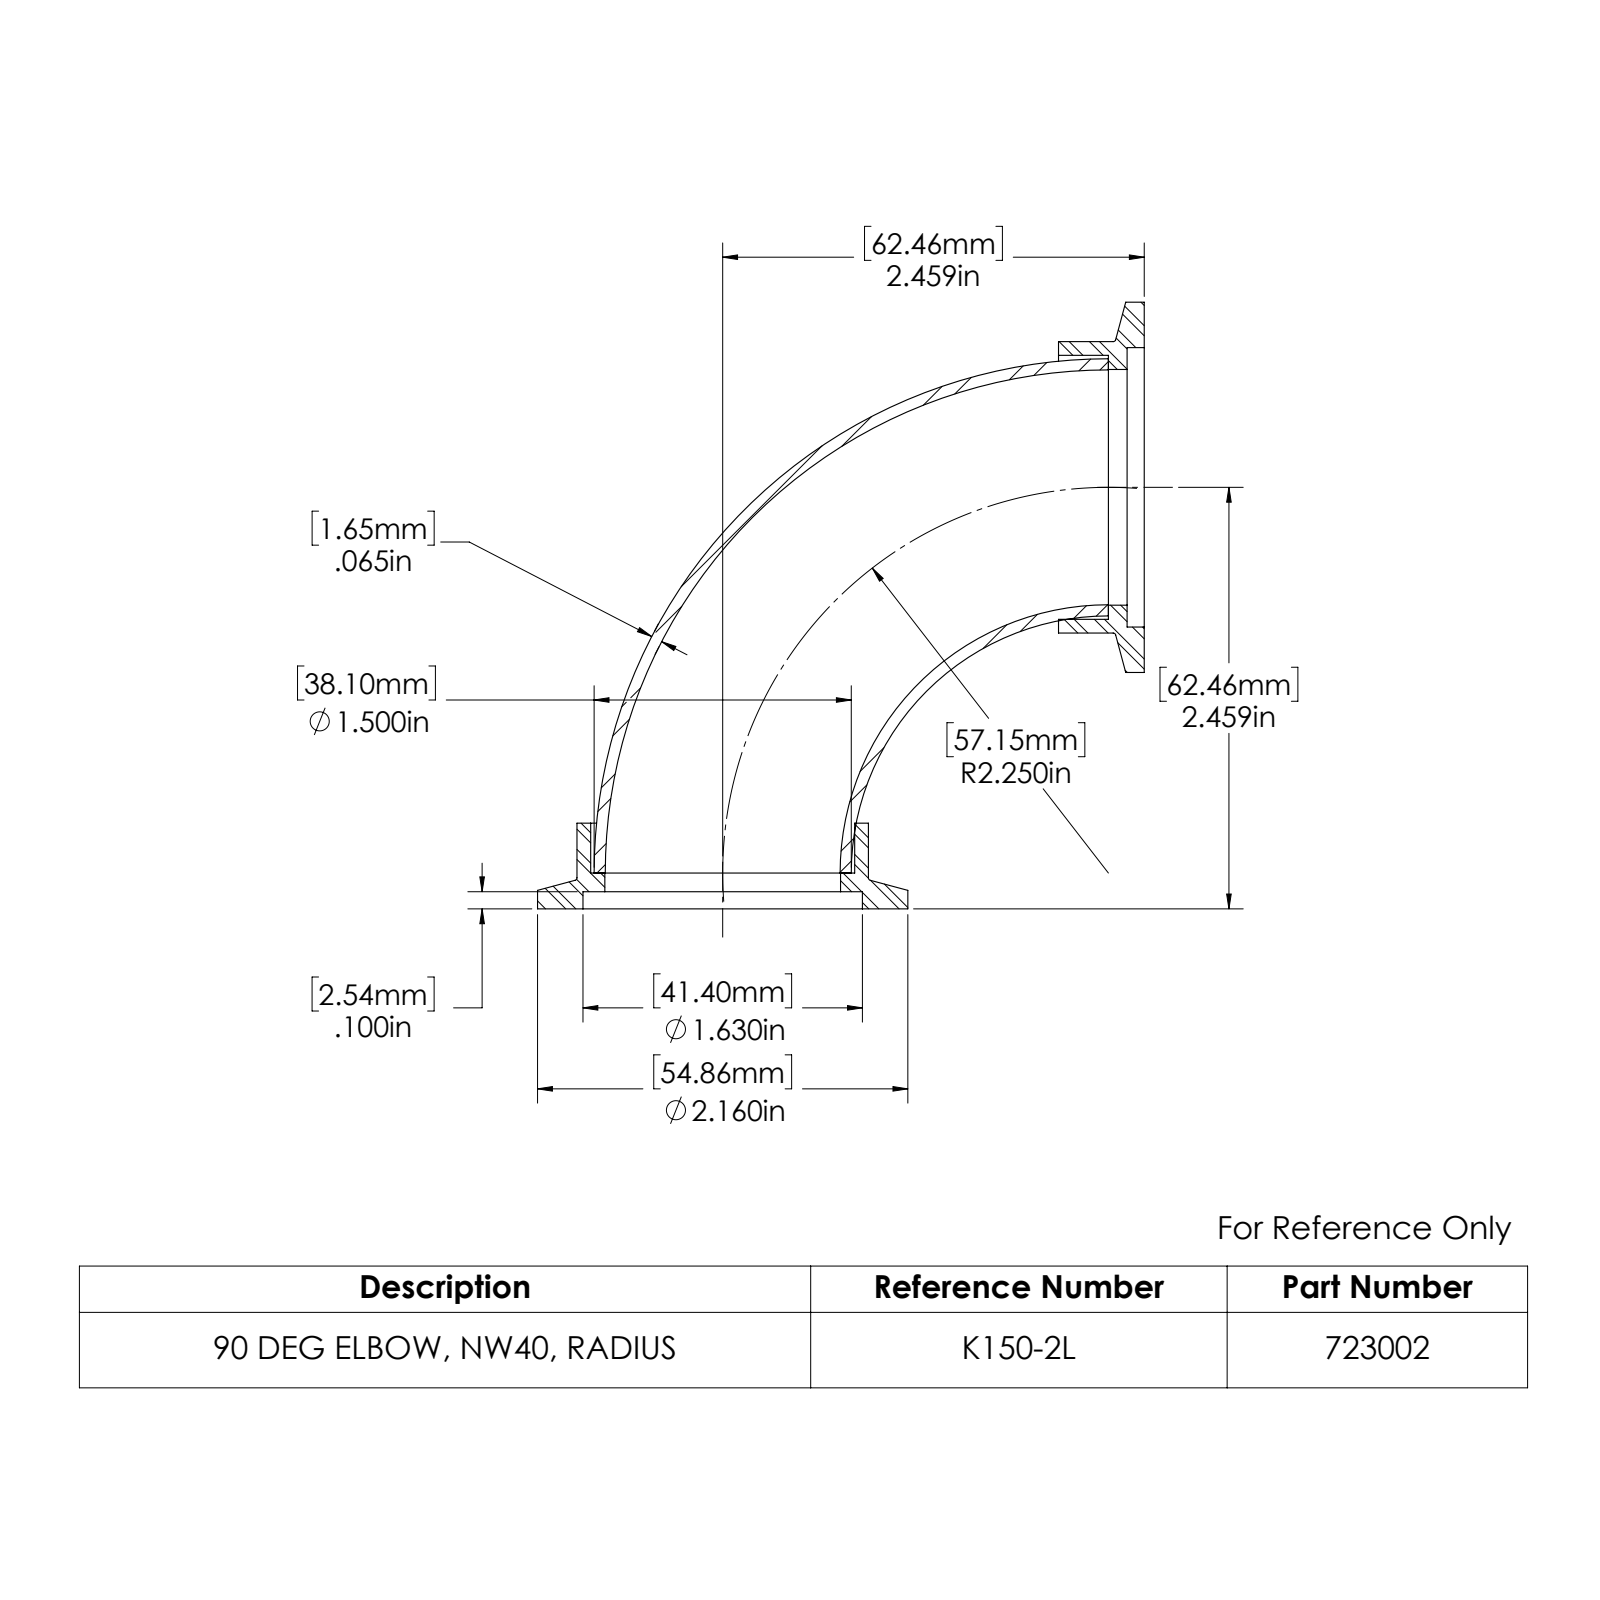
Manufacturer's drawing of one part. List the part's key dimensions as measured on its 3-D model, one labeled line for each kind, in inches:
Part name (STEP PRODUCT): 723002; 403502; 972302
STEP written by: SolidWorks 2022 (AUTOMOTIVE_DESIGN)
Units: inches
Bodies: 3 solids, 42 faces (10 planar, 20 cylindrical, 12 other)
Overall size (bounding box): 3.539 × 3.539 × 2.16
Volume: 1.864 in³ · Surface area: 51.01 in²
Round holes (diameter × count): ⌀1.375 ×2, ⌀1.54 ×2, ⌀1.63 ×2
Round bosses / shafts (diameter × count): ⌀2.16 ×2, ⌀1.7 ×2
Main face-to-face distances: 0.209, 0.1, 0.109, 0.5, 0.4, 0.291
